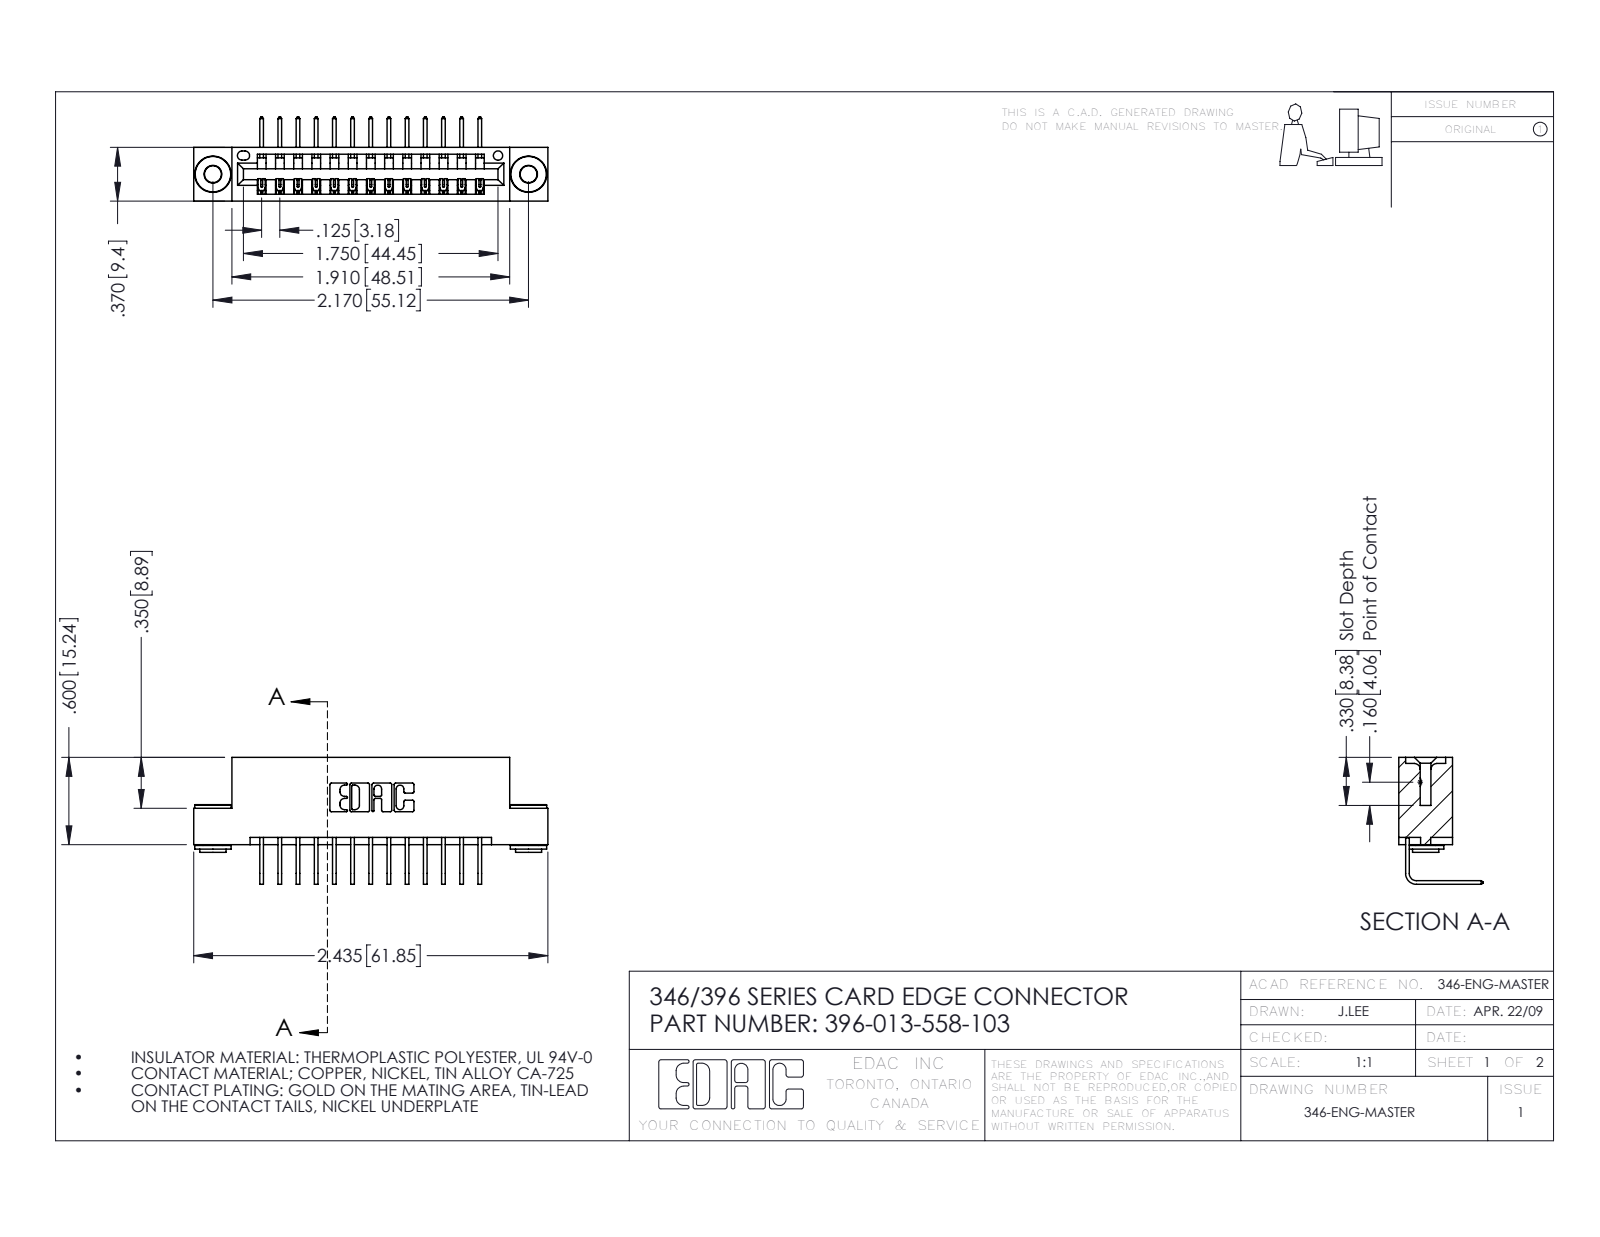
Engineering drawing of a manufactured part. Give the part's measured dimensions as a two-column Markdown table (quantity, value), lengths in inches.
| quantity | value |
| --- | --- |
| part name | 396-013-558-103; 345-292-001_558 Tail - 2; 345-250-002_345-250-002-102; 346 Part_Flush Mounting Lugs - 0.156 Dia-TH |
| STEP written by | SolidWorks 2016 (CONFIG_CONTROL_DESIGN) |
| units | inches |
| bodies | 16 solids, 940 faces (632 planar, 300 cylindrical, 8 other) |
| overall size | 2.435 × 0.873 × 0.58 |
| volume | 0.353 in³ |
| surface area | 11.46 in² |
| round holes (diameter × count) | 0.116 × 2, 0.156 × 2, 0.064 × 1 |
| round bosses / shafts (diameter × count) | 0.25 × 2, 0.18 × 2, 0.136 × 2 |
| partial cylindrical surfaces (radius × count) | 0.006 × 26, 0.01 × 22, 0.007 × 6, 0.031 × 6, 0.026 × 3, 0.031 × 2, 0.04 × 2, 0.014 × 1 |
| main face-to-face distances | 0.25, 0.322, 0.048, 0.37, 0.025, 0.298, 0.072, 0.148, 0.222, 0.1 |
| hole center spacings | 0.246, 1.964, 2.17 |
